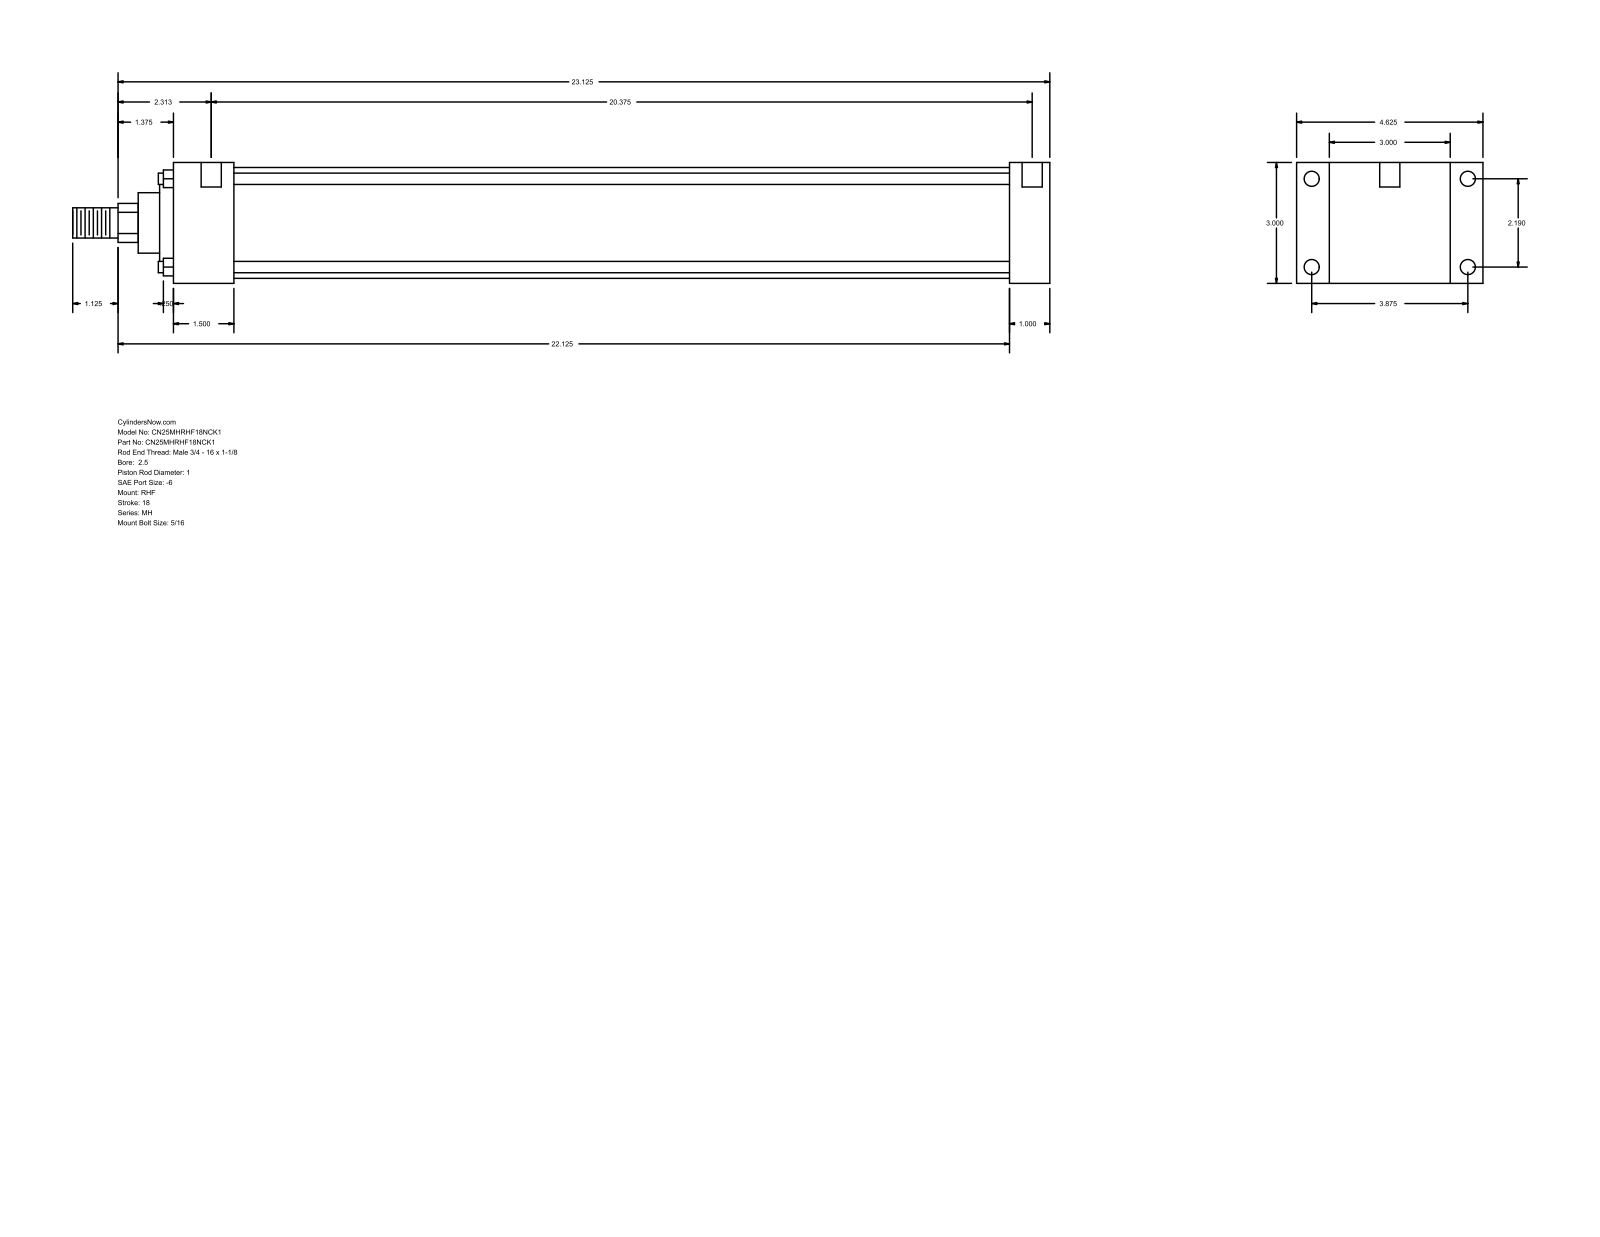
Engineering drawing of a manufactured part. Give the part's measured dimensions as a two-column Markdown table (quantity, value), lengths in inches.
| quantity | value |
| --- | --- |
| part name | MH_RHF__0250_1 |
| STEP written by | GSSL Pune (CONFIG_CONTROL_DESIGN) |
| units | inches |
| bodies | 0 solids, 90 faces (61 planar, 29 cylindrical, 0 other) |
| overall size | 24.25 × 4.625 × 3 |
| round holes (diameter × count) | 0.219 × 4, 0.375 × 4, 0.5 × 2 |
| round bosses / shafts (diameter × count) | 0.281 × 4, 2.75 × 1, 2.375 × 1, 1.5 × 1, 1 × 1, 0.75 × 1 |
| partial cylindrical surfaces (radius × count) | 0.484 × 1 |
| main face-to-face distances | 3, 1, 0.813, 3.813, 20.75, 21.75, 4.625, 1.5, 19.25, 20.25 |
| hole center spacings | 2.19, 3.875, 4.451, 20.687, 0.125, 0.187, 20.375, 20.5 |
